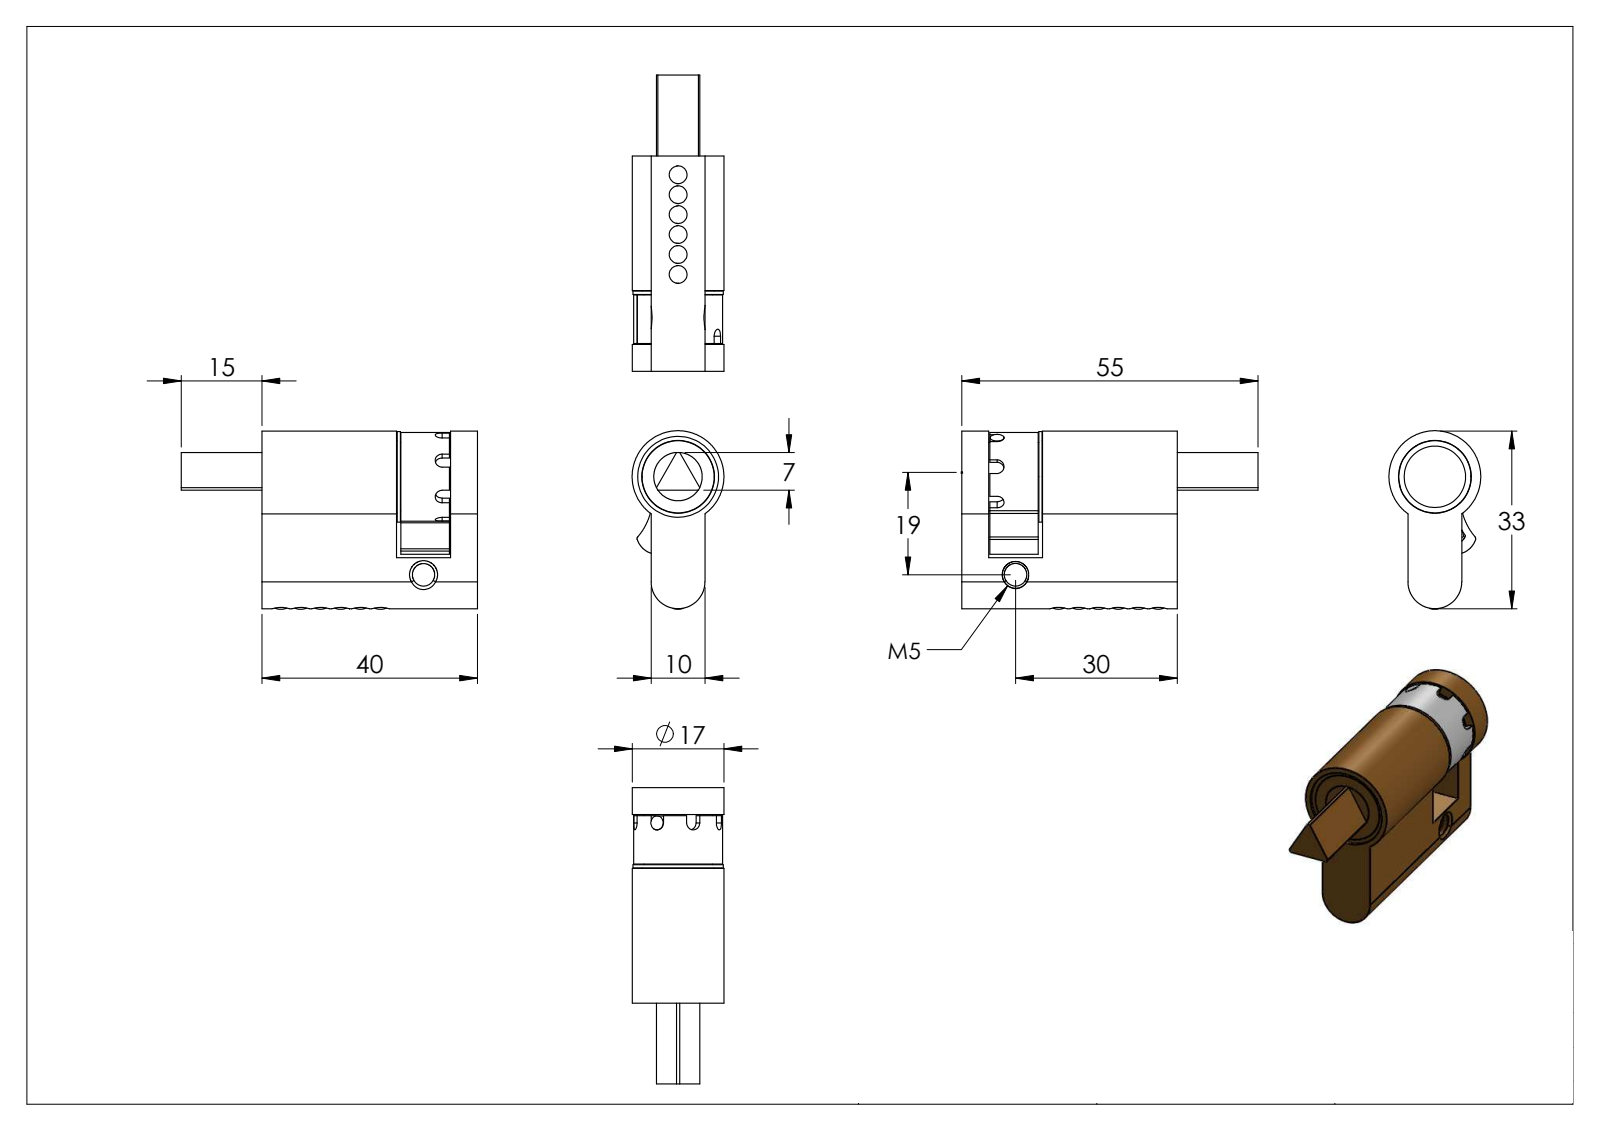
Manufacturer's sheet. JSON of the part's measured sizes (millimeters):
{"part_name": "859X Teil2; 859X Teil3_859X Teil3; 859X Teil1; 859X Teil2_8596 Teil2 (+5 more)", "step_written_by": "SolidWorks 2015 (CONFIG_CONTROL_DESIGN)", "units": "millimeters", "bodies": {"solids": 10, "faces": 284, "planar": 120, "cylindrical": 62, "other": 102}, "overall_size": [55, 33.1, 17], "volume_mm3": 13921, "surface_area_mm2": 10072, "round_holes": [[3.3, 6], [2.6, 3], [4.2, 1], [12.7, 1], [13.5, 1], [15, 1]], "round_bosses_or_shafts": [[17, 1], [16.8, 1], [16.5, 1], [13.4, 1], [9, 1]], "partial_cylinders_radius": [[1.3, 5], [0.5, 4], [11, 2], [12.3, 2], [2, 1], [4, 1], [5, 1], [6.85, 1]], "face_to_face_distances": [10, 40, 15, 0.7, 5, 35, 25, 14.2, 9.2, 0.8], "hole_center_spacings": [3.7, 7.4, 11.1, 14.8, 18.5]}
